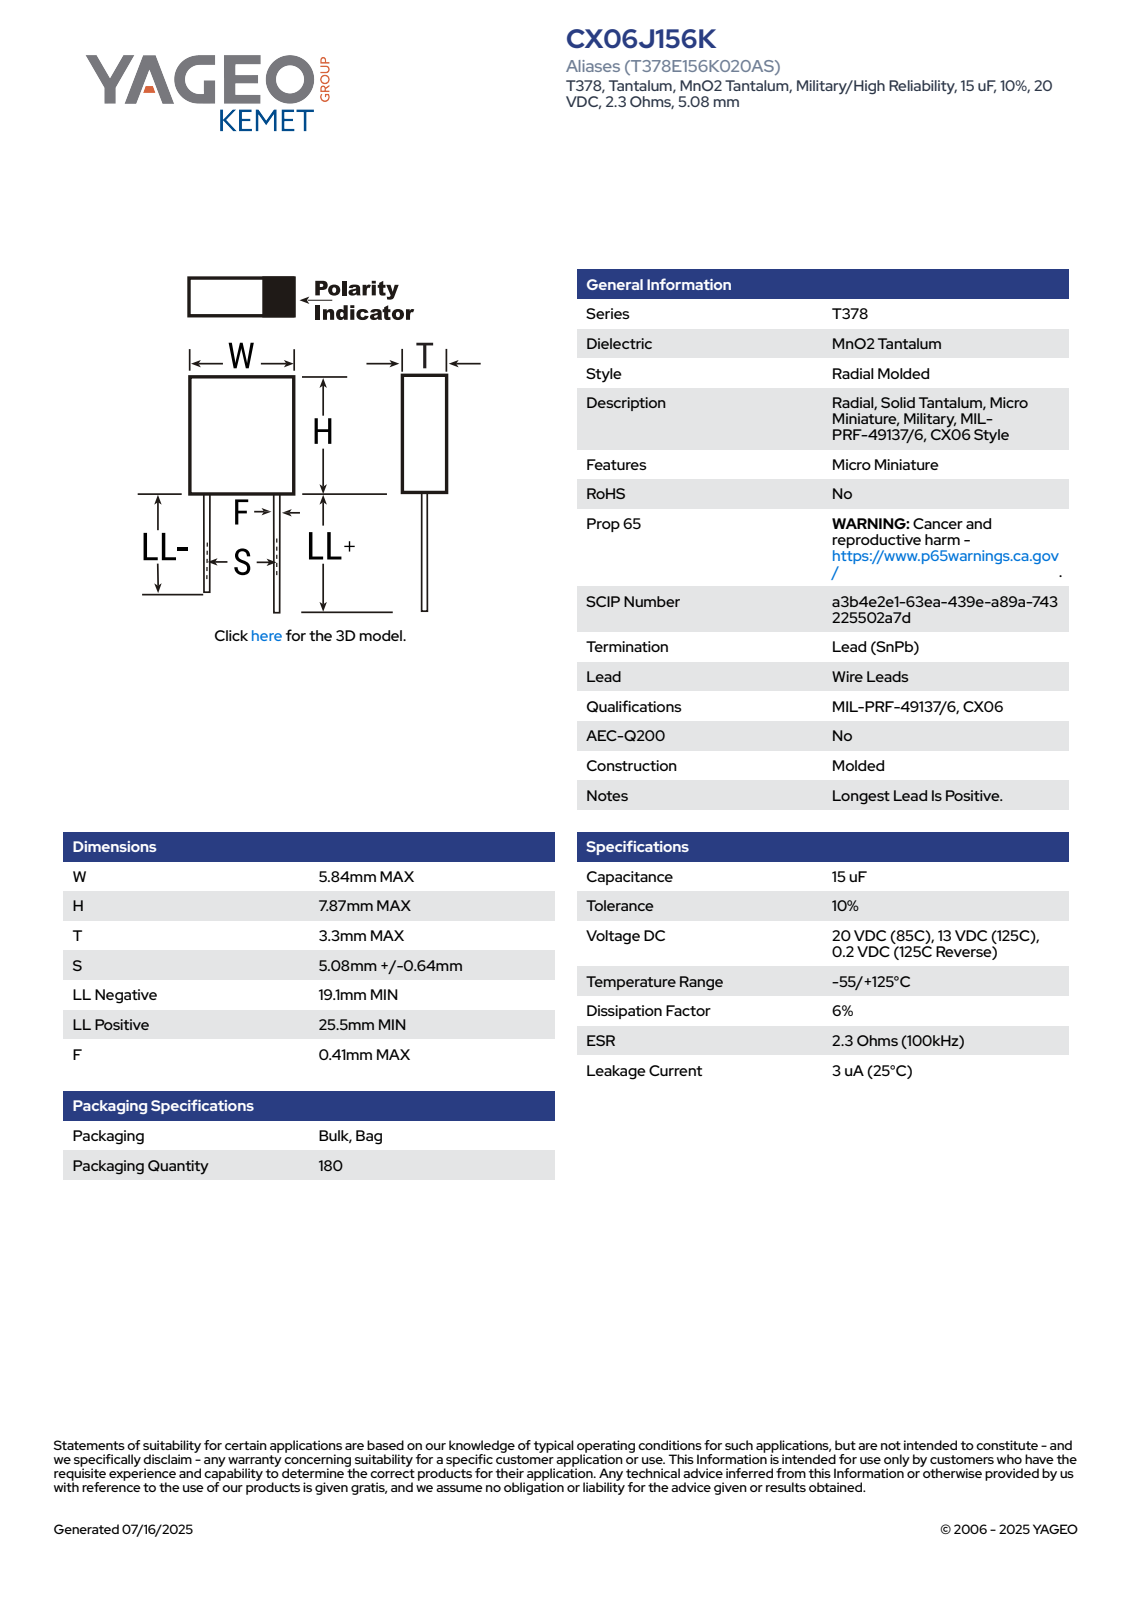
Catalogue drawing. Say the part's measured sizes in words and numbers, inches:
The part is named "CTRM_T378_W5.84H7.87T3.3S5.08LL44.46F0.44". Its 3-D file was written by "SolidWorks 2014 (AUTOMOTIVE_DESIGN)". It is 4 solids with 71 faces: 67 planar, 4 cylindrical and 0 other. Overall it measures 2.06 by 0.23 by 0.13 inches. Its volume is 0.01 cubic inches and its surface area 0.468 square inches. Round bosses or shafts: 2 of diameter 0.017. The main face-to-face distances are 0.13, 0.23, 0.31, 1.5, 1.81, 0.25, 1.75, 2.06, 0.115, 1.924.
